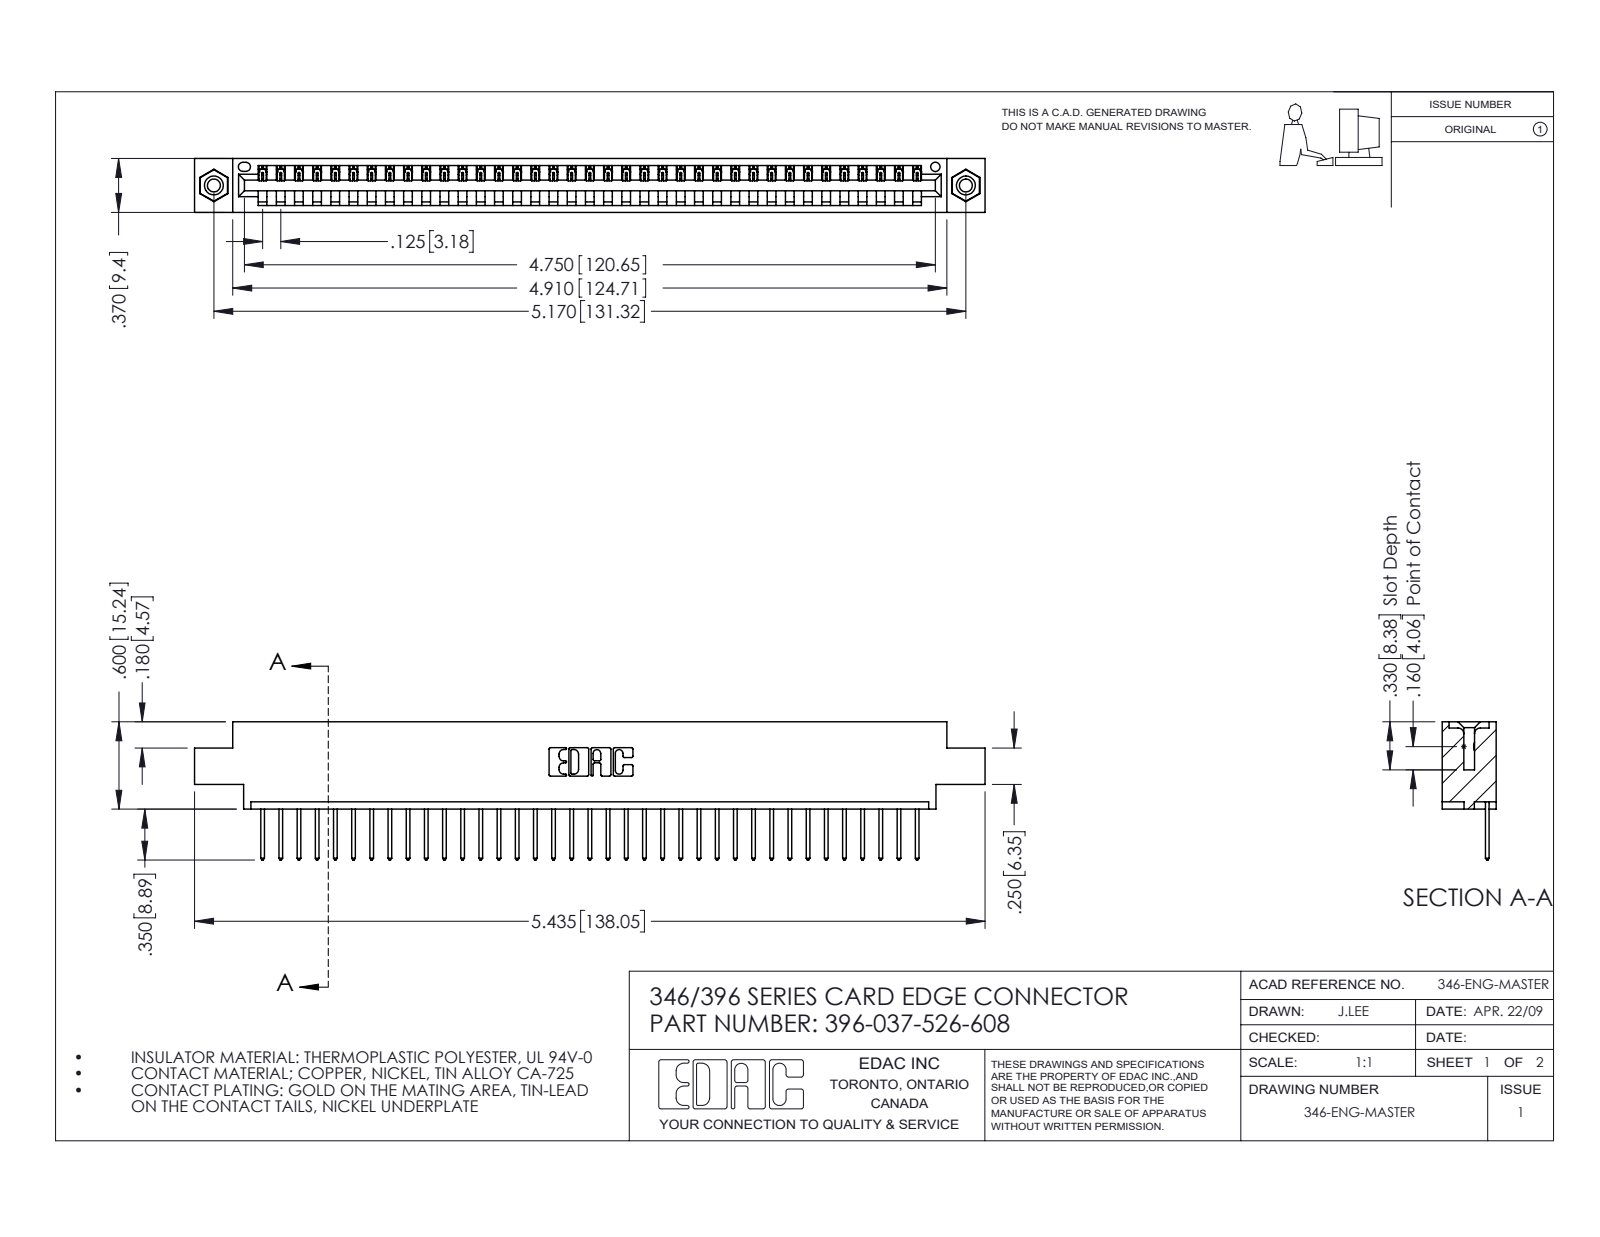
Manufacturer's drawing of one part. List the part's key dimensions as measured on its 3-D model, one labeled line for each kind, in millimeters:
Part name (STEP PRODUCT): 396-037-526-608; 345-292-001_345-293-126; 346 Part_0.170 Offset - 0.156 Dia-TI; 345-250-001_345-250-003-102
STEP written by: SolidWorks 2016 (CONFIG_CONTROL_DESIGN)
Units: millimetres
Bodies: 40 solids, 2332 faces (1592 planar, 724 cylindrical, 16 other)
Overall size (bounding box): 138 × 24.1 × 9.4
Volume: 13 000 mm³ · Surface area: 16 330 mm²
Round holes (diameter × count): ⌀2.3 ×2, ⌀3.2 ×2, ⌀4 ×2, ⌀1.6 ×1
Round bosses / shafts (diameter × count): ⌀3.9 ×2
Partial cylindrical surfaces — rounded edges, fillets, slot ends (radius × count): R0.2 ×74, R0.3 ×74, R0.3 ×22, R0.2 ×6, R0.8 ×6, R0.7 ×3, R0.8 ×2, R1 ×2
Main face-to-face distances: 1.2, 8.2, 9.4, 6.4, 1.8, 7.6, 0.6, 5.6, 3.8, 2.5
Hole centre spacings: 6.2, 126, 131.3
